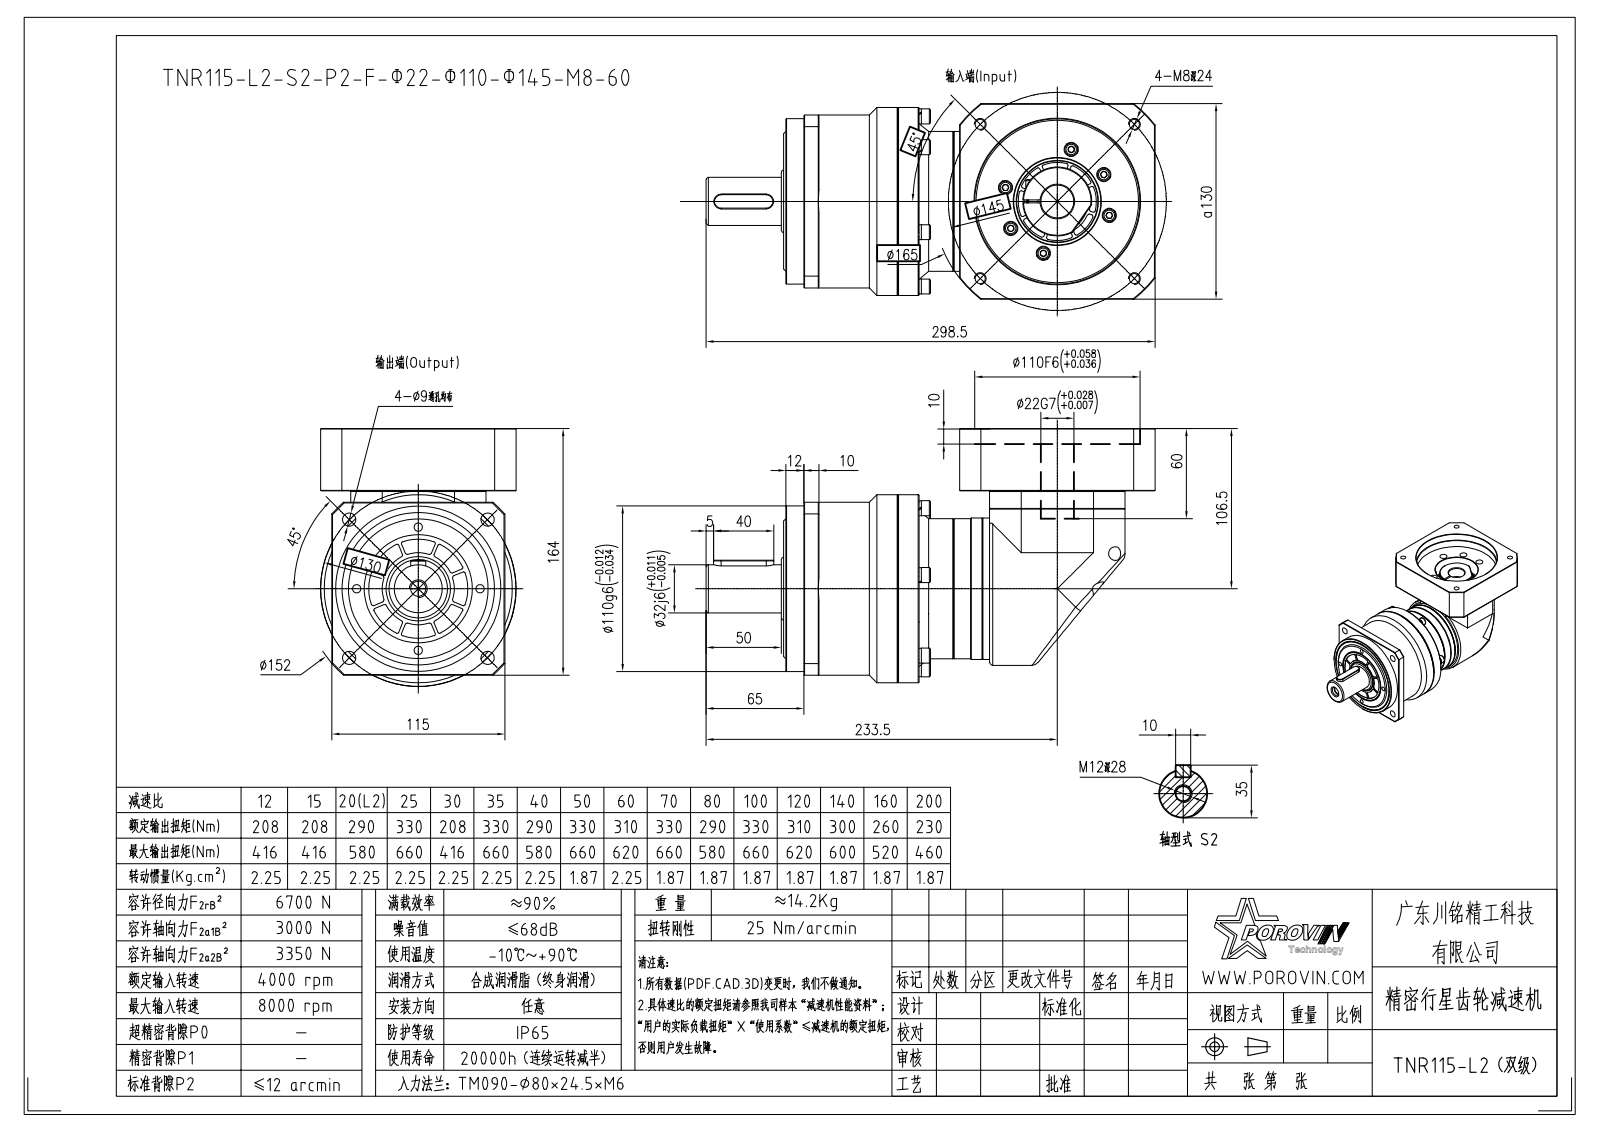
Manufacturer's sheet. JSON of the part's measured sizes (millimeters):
{"part_name": "20001; 5_5__5_5__1000; TN115_0001_ASM; HEXAGON_SOCKET_HEAD_CAP_SC-5945 (+8 more)", "step_written_by": "CREO PARAMETRIC BY PTC INC, 2020053 (CONFIG_CONTROL_DESIGN)", "units": "millimeters", "bodies": {"solids": 62, "faces": 1620, "planar": 674, "cylindrical": 646, "other": 300}, "overall_size": [298.5, 169, 130], "volume_mm3": 2487000, "surface_area_mm2": 318960, "round_holes": [[5.4, 19], [5.5, 17], [9.5, 12], [9.2, 7], [4.2, 6], [6.6, 6], [6.68, 6], [5, 5], [6.8, 4], [9, 4], [10.2, 2], [6.5, 1]], "round_bosses_or_shafts": [[8.5, 19], [8, 19], [5, 19], [10, 7], [6, 7], [9.88, 6], [125, 1], [115, 1]], "partial_cylinders_radius": [[1, 76], [5, 3], [4, 1], [5.25, 1], [51, 1], [76, 1], [82.5, 1]], "face_to_face_distances": [20, 37, 12, 56.5, 19.5, 56.3, 19.3, 130, 110, 21.5], "hole_center_spacings": [35.75, 57.25, 40.75, 46.18, 98.8, 39.08, 46.25, 58.16]}
